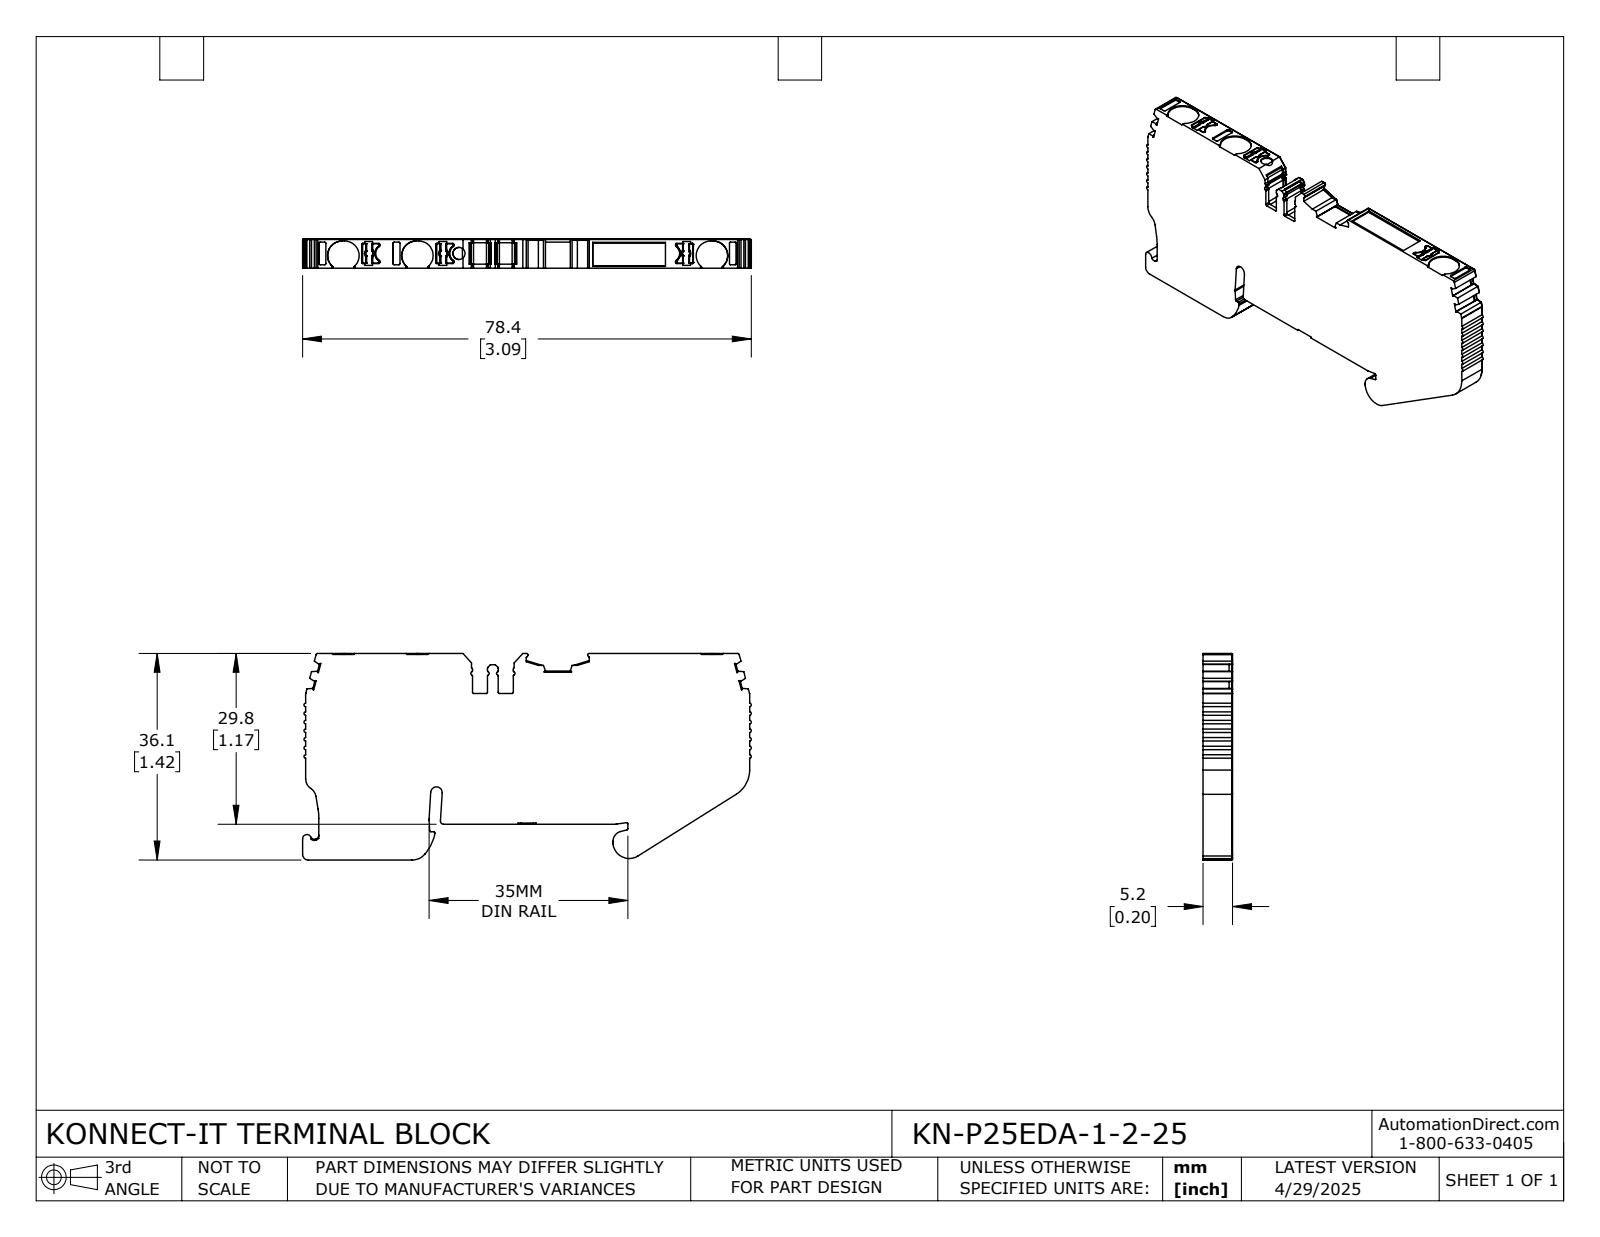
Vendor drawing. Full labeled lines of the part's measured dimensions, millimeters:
Part name (STEP PRODUCT): KN-P25EDA-1-2-25
STEP written by: SolidWorks 2024 (CONFIG_CONTROL_DESIGN)
Units: millimetres
Bodies: 1 solid, 665 faces (349 planar, 265 cylindrical, 51 other)
Overall size (bounding box): 78.36 × 36.07 × 5.15
Volume: 11 968 mm³ · Surface area: 6 211 mm²
Round holes (diameter × count): ⌀2.1 ×1
Partial cylindrical surfaces — rounded edges, fillets, slot ends (radius × count): R0.2 ×66, R0.3 ×39, R0.1 ×19, R0.5 ×18, R0.15 ×12, R0.4 ×9, R2.55 ×6, R1 ×3
Main face-to-face distances: 5.15, 29.61, 29.81, 6.26, 35.87, 36.07, 77.52, 1.2, 5, 4.5
